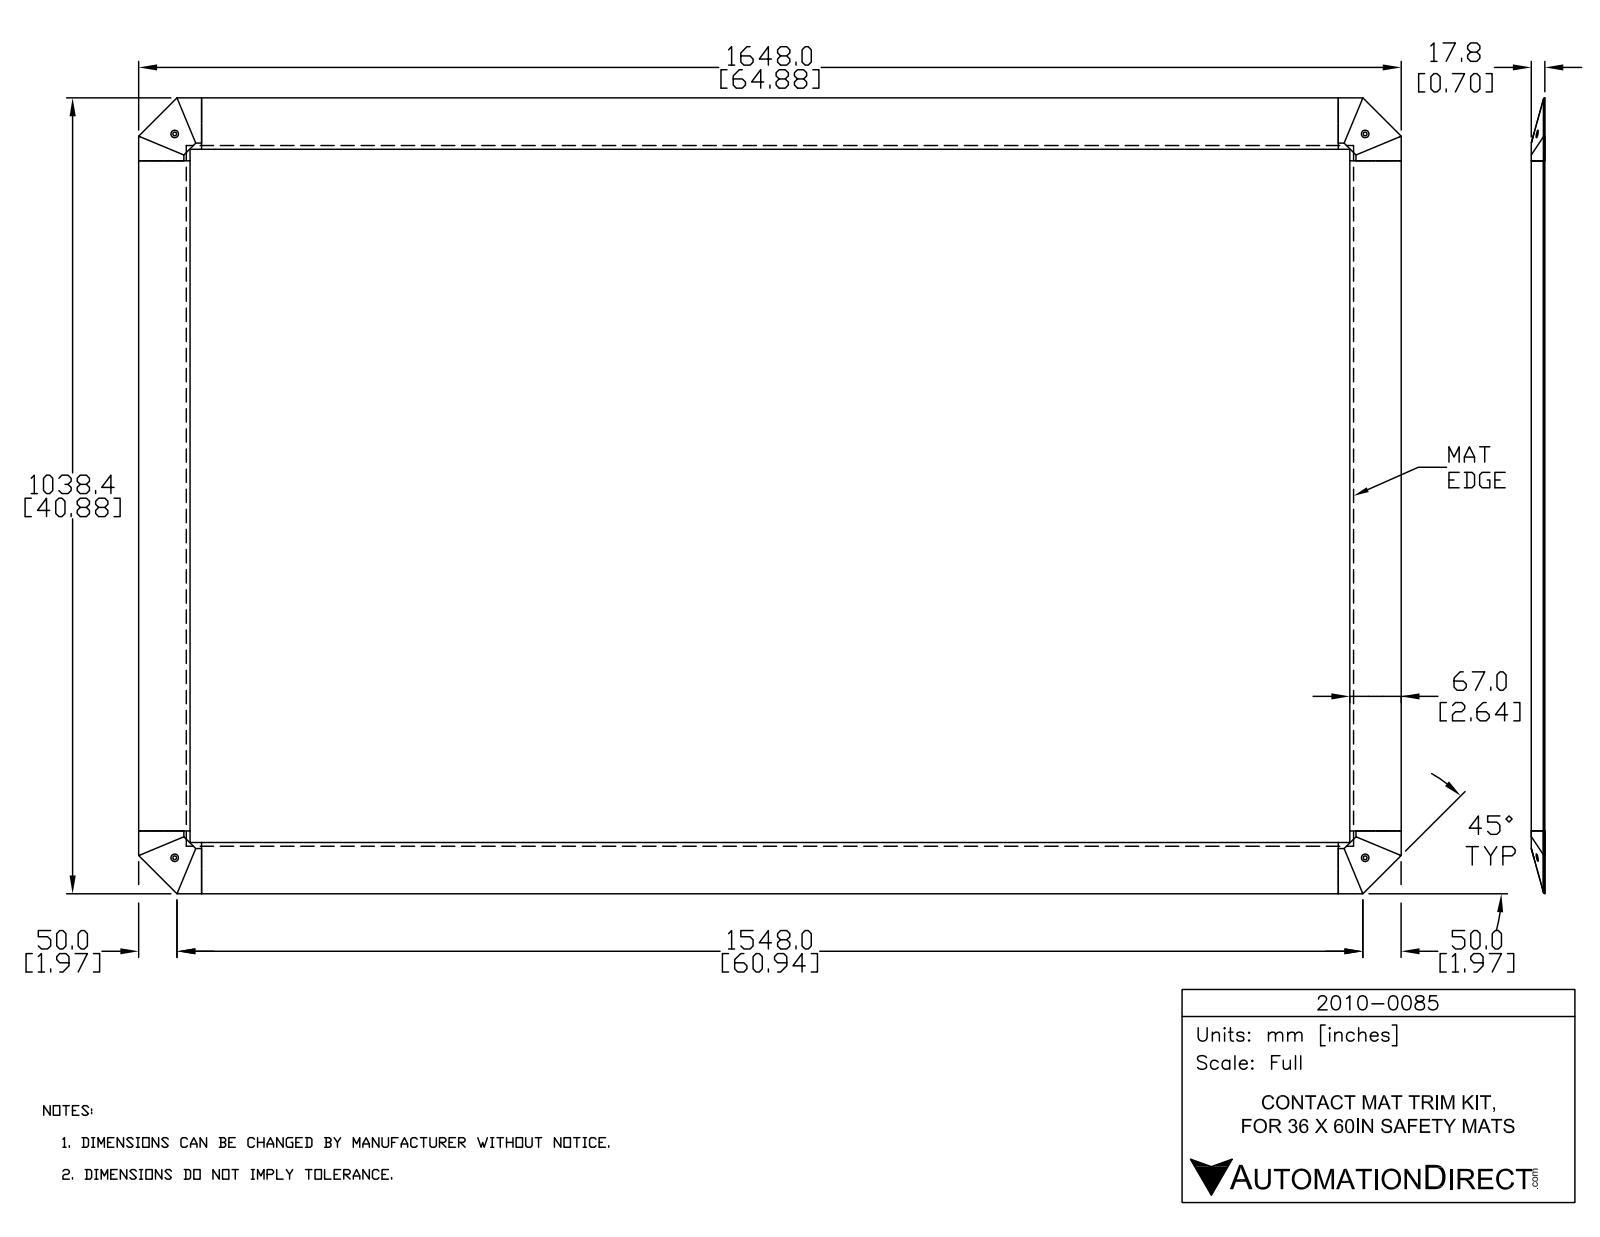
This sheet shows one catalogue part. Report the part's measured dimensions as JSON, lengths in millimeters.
{"part_name": "2010-0085", "step_written_by": "SolidWorks 2018 (AUTOMOTIVE_DESIGN)", "units": "millimeters", "bodies": {"solids": 1, "faces": 2109, "planar": 1613, "cylindrical": 440, "other": 56}, "overall_size": [1648, 1038.4, 17.8], "volume_mm3": 1462000, "surface_area_mm2": 1137000, "round_holes": [[5, 4], [9.8, 4]], "round_bosses_or_shafts": [[10, 4]], "partial_cylinders_radius": [[0.2, 200], [1, 108], [0.5, 60], [0.4, 8], [13, 8], [7.4, 4], [10, 4]], "face_to_face_distances": [2.9, 1.9, 4.8, 1, 3, 16, 7.7, 1, 2, 19], "hole_center_spacings": [944.4, 1554, 1818.5]}
